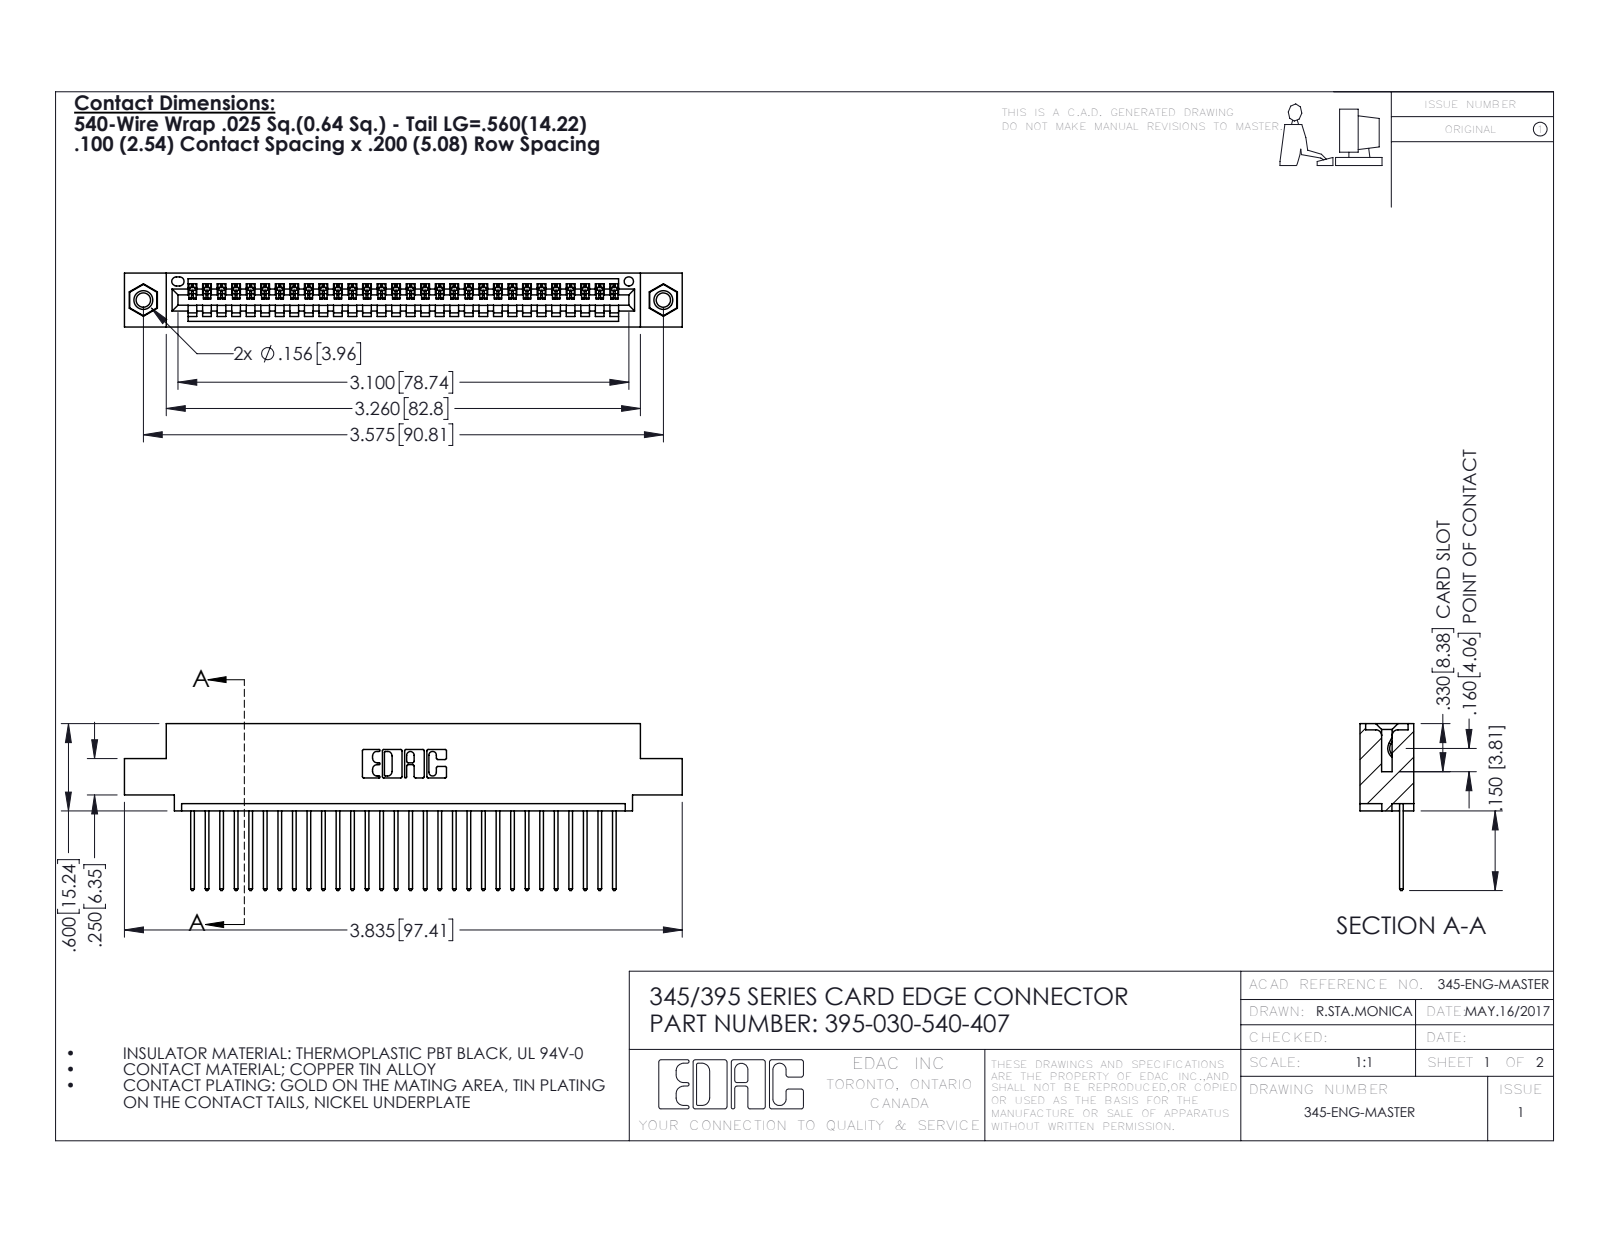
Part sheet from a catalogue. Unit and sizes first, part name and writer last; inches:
Units: inches
Overall size (bounding box): 3.835 × 1.147 × 0.37
Round holes (diameter × count): ⌀0.098 ×2, ⌀0.125 ×2, ⌀0.156 ×2, ⌀0.064 ×1
Round bosses / shafts (diameter × count): ⌀0.155 ×2
Partial cylindrical surfaces — rounded edges, fillets, slot ends (radius × count): R0.006 ×60, R0.01 ×60, R0.01 ×22, R0.007 ×6, R0.031 ×6, R0.026 ×3, R0.031 ×2, R0.04 ×2
Main face-to-face distances: 0.072, 0.298, 0.37, 0.2, 0.098, 0.272, 0.025, 0.225, 0.149, 0.072
Hole centre spacings: 0.27, 3.34, 3.575
Volume: 0.556 in³ · Surface area: 19.14 in²
Bodies: 33 solids, 1930 faces (1316 planar, 598 cylindrical, 16 other)
Part name (STEP PRODUCT): 345-250-001_345-250-005-103; 345-292-001_345-293-140; 345 Part_0.110 Offset - 0.156 Dia-TI; 395-030-540-407
STEP written by: SolidWorks 2016 (CONFIG_CONTROL_DESIGN)
